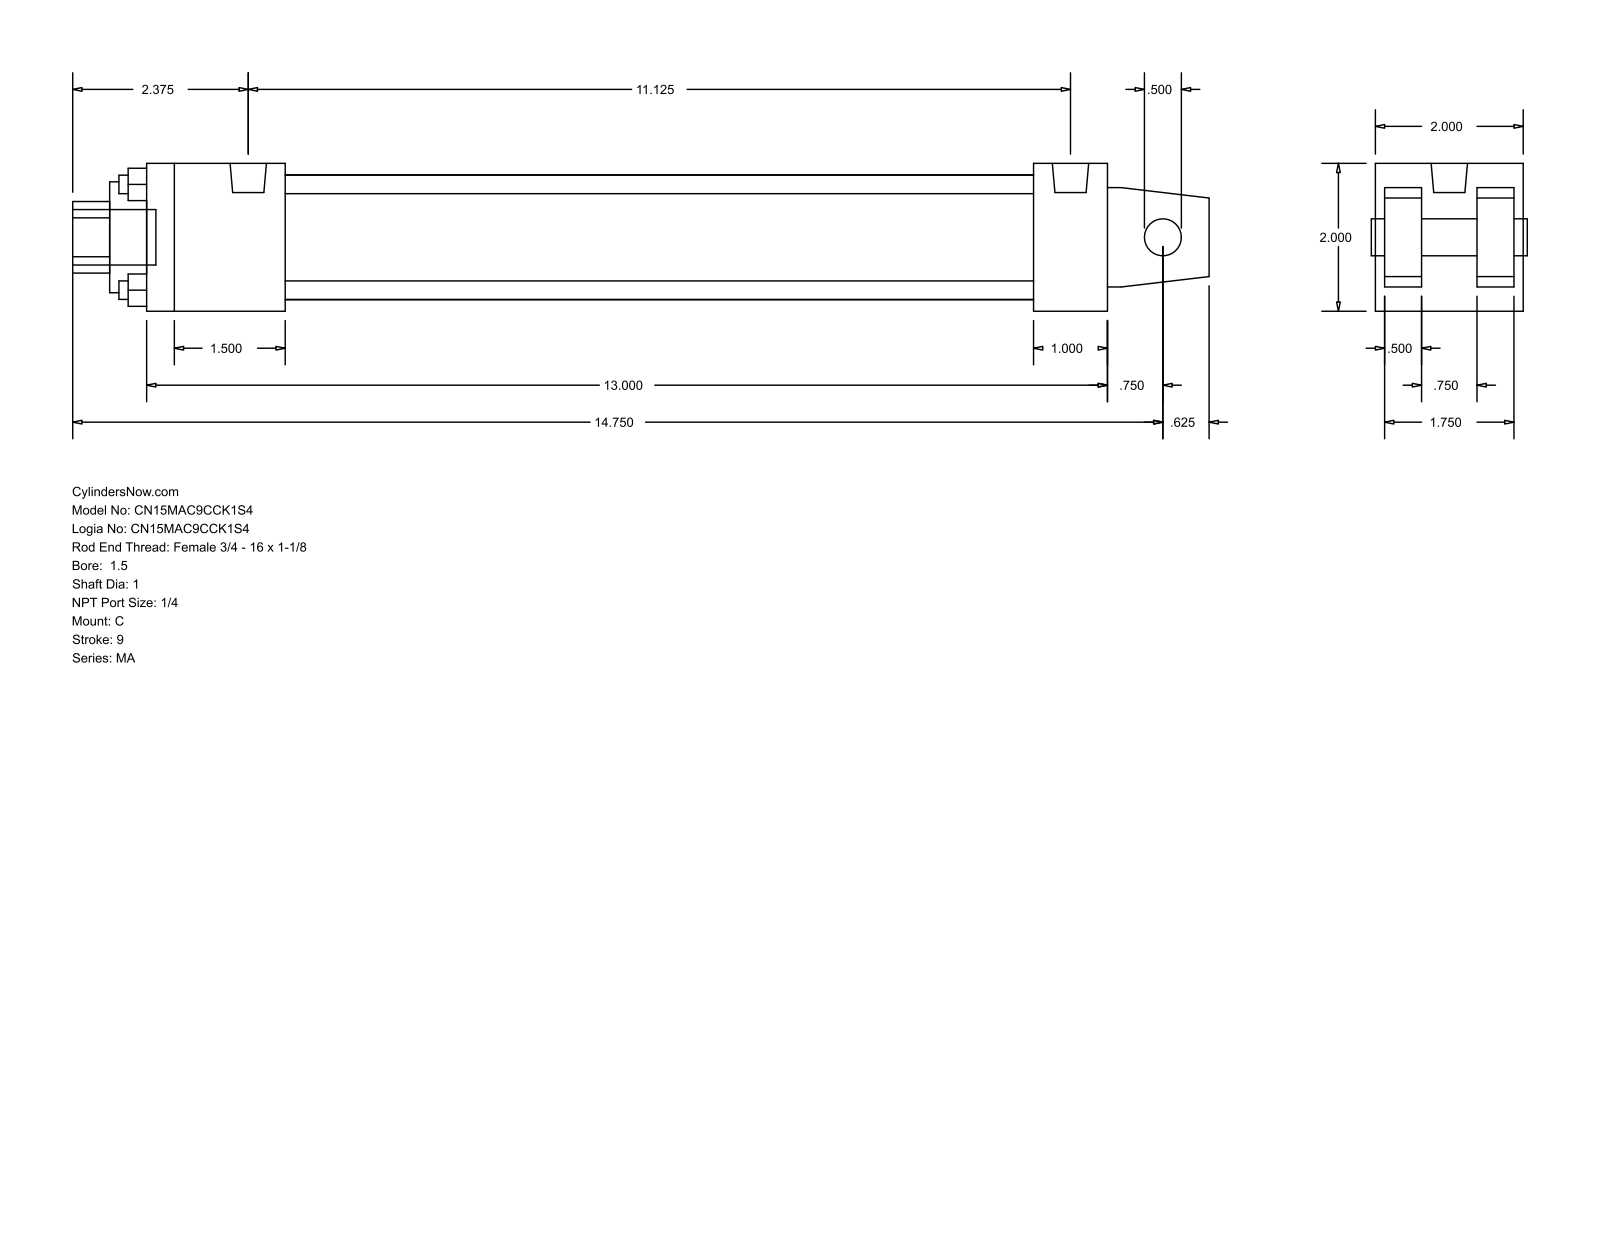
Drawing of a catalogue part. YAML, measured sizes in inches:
part_name: "MA_C__0150_1"
step_written_by: "GSSL Pune (CONFIG_CONTROL_DESIGN)"
units: inches
bodies: {solids: 0, faces: 103, planar: 76, cylindrical: 27, other: 0}
overall_size: [15.375, 2, 2]
round_holes:
  - {diameter: 0.25, count: 4}
  - {diameter: 0.5, count: 1}
  - {diameter: 1, count: 1}
  - {diameter: 1.5, count: 1}
  - {diameter: 1.69, count: 1}
round_bosses_or_shafts:
  - {diameter: 0.313, count: 4}
  - {diameter: 0.492, count: 2}
  - {diameter: 0.75, count: 1}
partial_cylinders:
  - {radius: 0.484, count: 1}
face_to_face_distances: [2, 1.875, 0.5, 0.125, 0.625, 1.375, 1.25, 1.75, 13, 1]
hole_center_spacings: [1.011, 1.43, 2.022]
